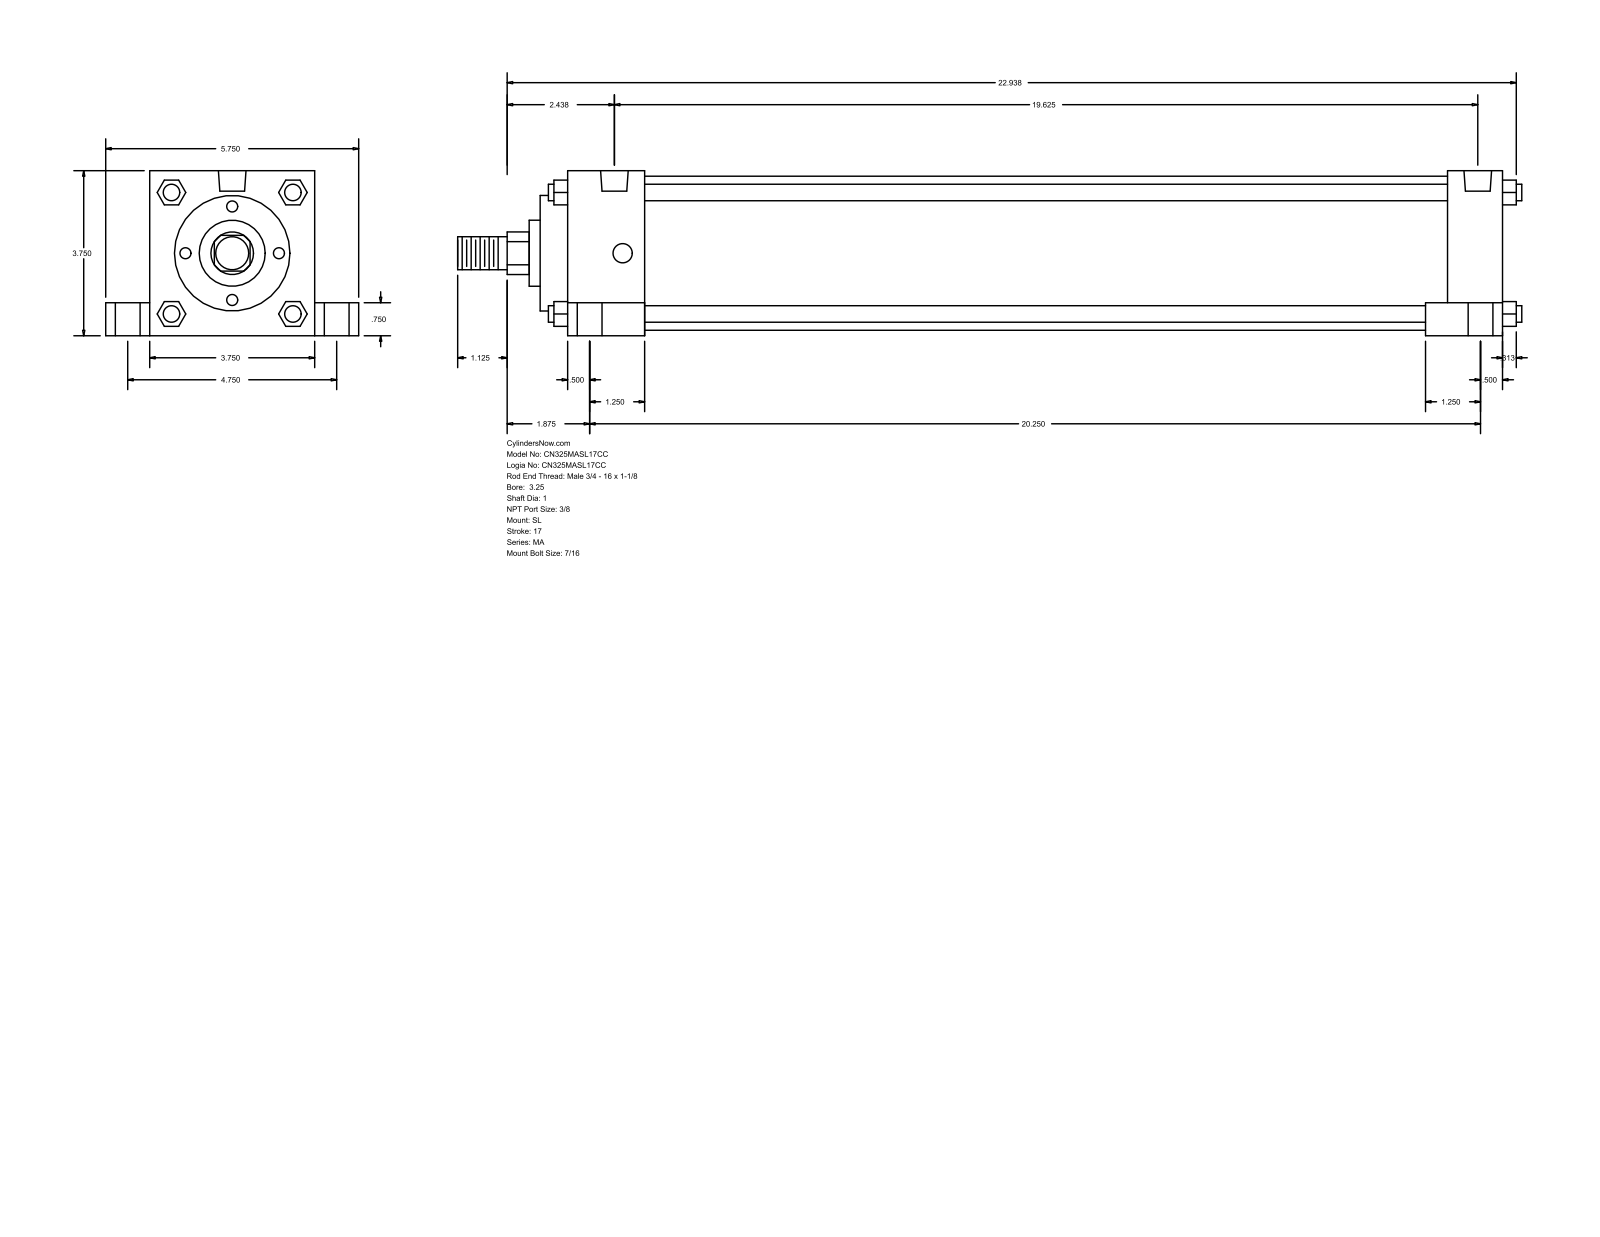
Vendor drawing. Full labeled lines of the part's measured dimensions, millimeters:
Part name (STEP PRODUCT): MA_SL__0325_1
STEP written by: GSSL Pune (CONFIG_CONTROL_DESIGN)
Units: millimetres
Bodies: 0 solids, 150 faces (113 planar, 37 cylindrical, 0 other)
Overall size (bounding box): 614.36 × 146.05 × 95.25
Round holes (diameter × count): ⌀11.11 ×4, ⌀14.29 ×4, ⌀20.64 ×4, ⌀15.93 ×2
Round bosses / shafts (diameter × count): ⌀9.53 ×4, ⌀88.9 ×1, ⌀66.67 ×1, ⌀38.1 ×1, ⌀25.4 ×1, ⌀19.05 ×1
Partial cylindrical surfaces — rounded edges, fillets, slot ends (radius × count): R12.29 ×1
Main face-to-face distances: 95.24, 539.75, 15.87, 25.41, 120.65, 555.62, 19.05, 508, 31.75, 44.46
Hole centre spacings: 60.35, 60.66, 62, 63.27, 120.66, 488.95, 498.97, 503.7
